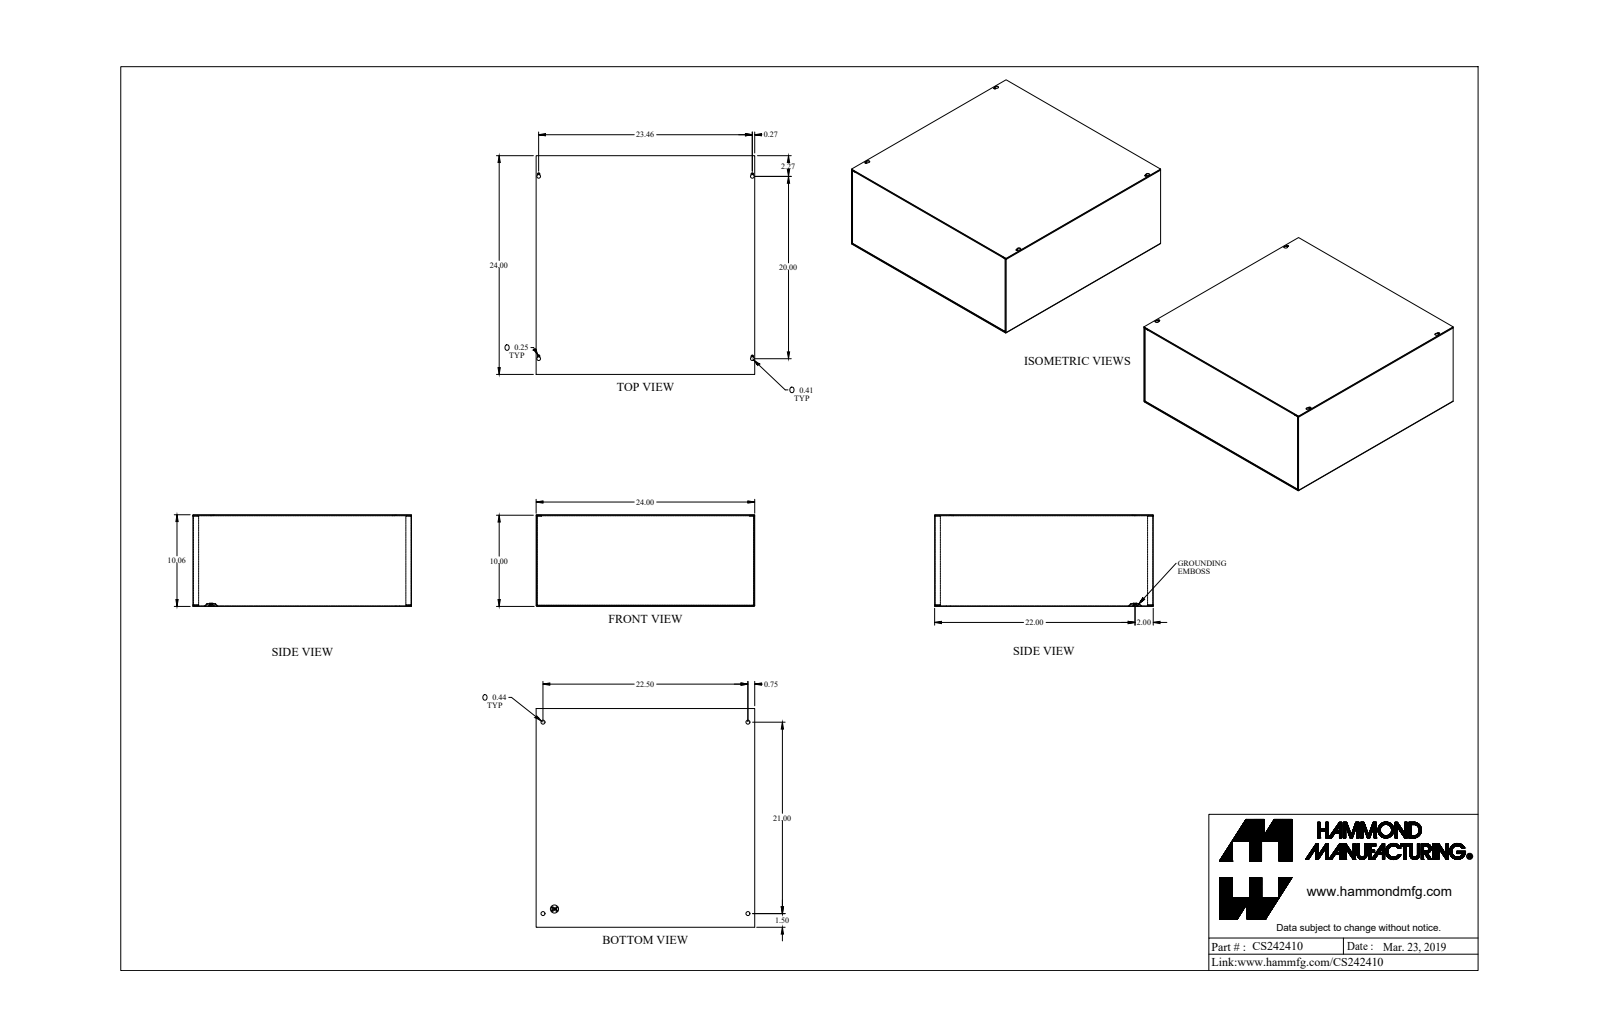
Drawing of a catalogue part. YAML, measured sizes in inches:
part_name: "CS242410_Default"
step_written_by: "SolidWorks 2019 (CONFIG_CONTROL_DESIGN)"
units: inches
bodies: {solids: 4, faces: 205, planar: 125, cylindrical: 72, other: 8}
overall_size: [24, 24, 10.057]
volume: 124.6
surface_area: 4395
round_holes:
  - {diameter: 0.17, count: 5}
  - {diameter: 0.437, count: 4}
  - {diameter: 0.5, count: 1}
round_bosses_or_shafts:
  - {diameter: 0.492, count: 1}
  - {diameter: 0.284, count: 1}
partial_cylinders:
  - {radius: 0.029, count: 12}
  - {radius: 0.086, count: 12}
  - {radius: 0.057, count: 8}
  - {radius: 0.125, count: 4}
  - {radius: 0.203, count: 4}
face_to_face_distances: [0.057, 10, 23.943, 9.943, 10.057, 24, 23.886, 0.08, 9.863, 9.92]
hole_center_spacings: [0.693, 20.506, 22.985, 30.795, 20, 21, 22.5, 23.46]
